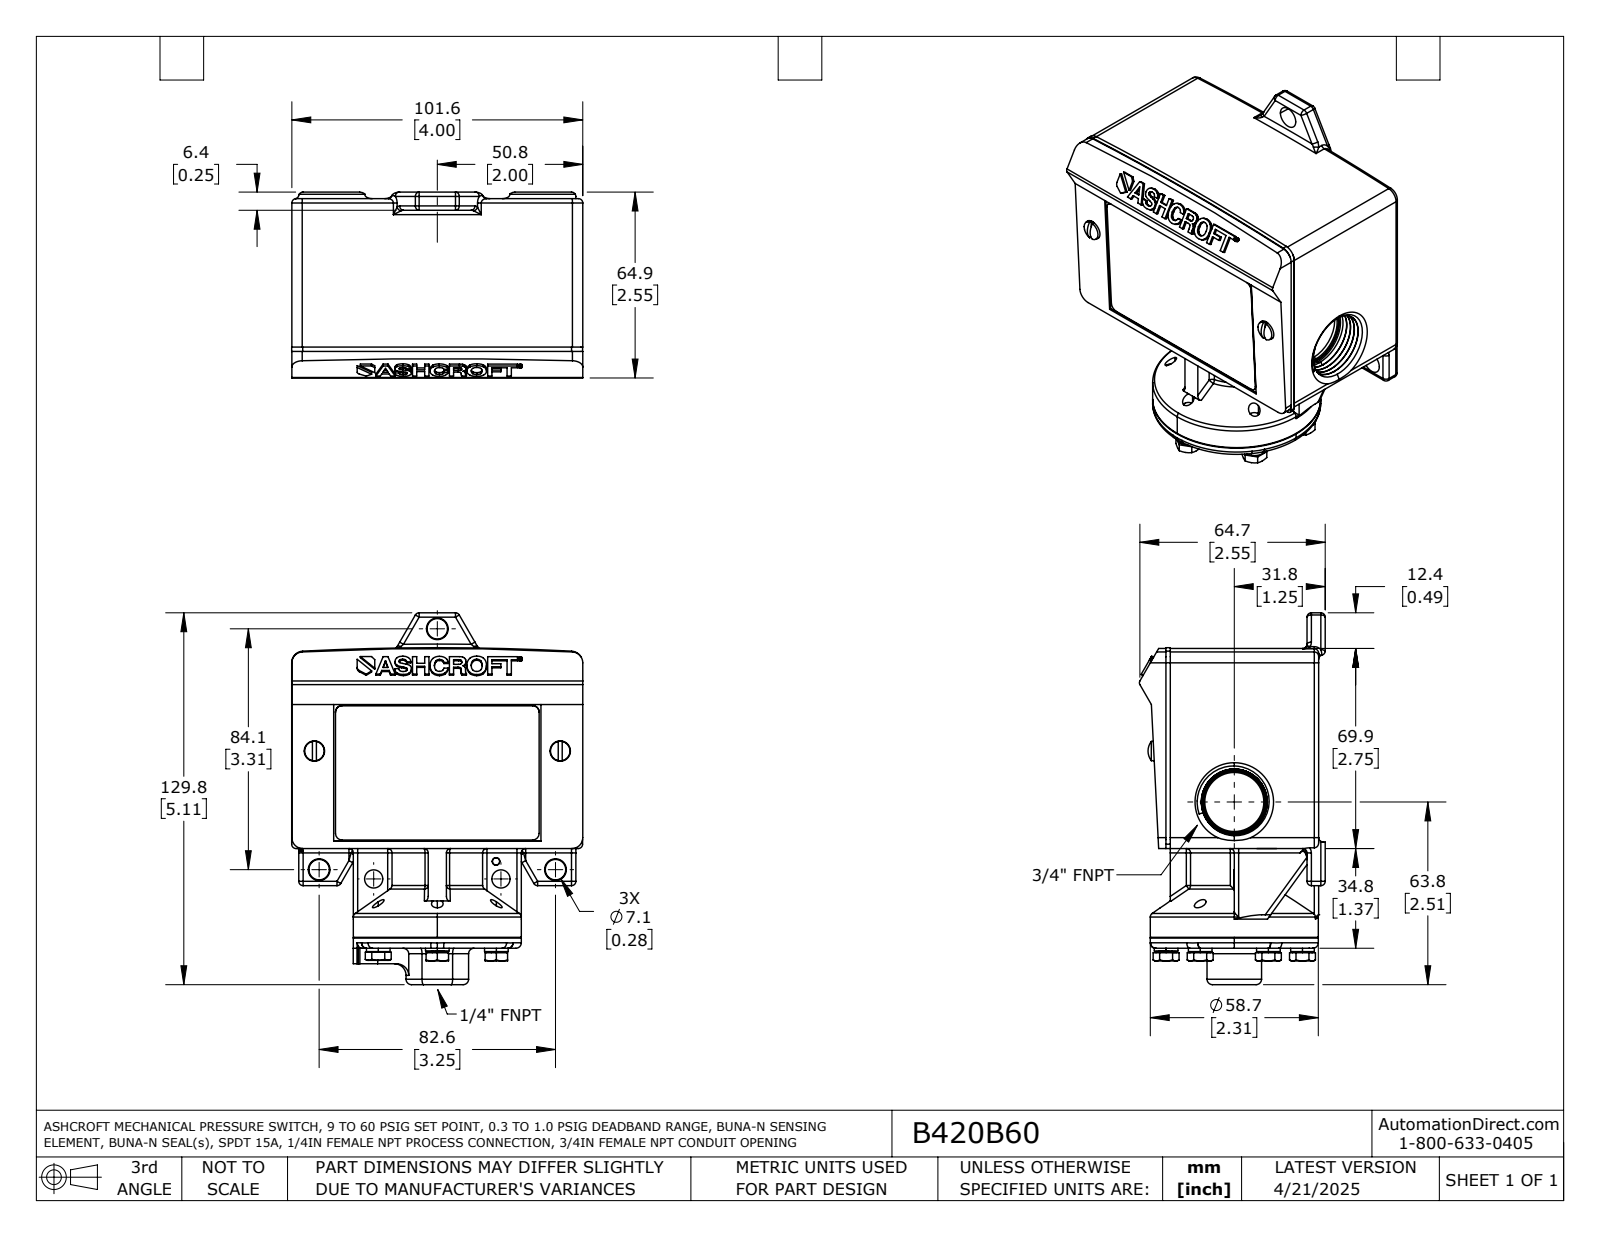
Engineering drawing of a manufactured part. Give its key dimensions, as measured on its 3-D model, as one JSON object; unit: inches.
{"part_name": "B420B60", "step_written_by": "SolidWorks 2021 (AUTOMOTIVE_DESIGN)", "units": "inches", "bodies": {"solids": 2, "faces": 1259, "planar": 345, "cylindrical": 472, "other": 442}, "overall_size": [5.111, 4.003, 2.555], "volume_in3": 28.57, "surface_area_in2": 84.51, "round_holes": [[0.161, 6], [0.192, 5], [0.209, 5], [0.187, 4], [0.28, 2], [0.455, 1], [0.812, 1]], "round_bosses_or_shafts": [[0.325, 6], [0.278, 6], [0.19, 5], [0.27, 2], [0.25, 2], [2.31, 1]], "partial_cylinders_radius": [[0.06, 92], [0.03, 5], [0.075, 4], [0.09, 4], [0.15, 4], [0.01, 2], [0.094, 2], [0.16, 2]], "face_to_face_distances": [4, 0.015, 1.37, 0.09, 3.91, 0.44, 3.56, 3.47, 0.35, 0.845], "hole_center_spacings": [0.937, 1.624, 1.875, 0.938, 3.38]}
